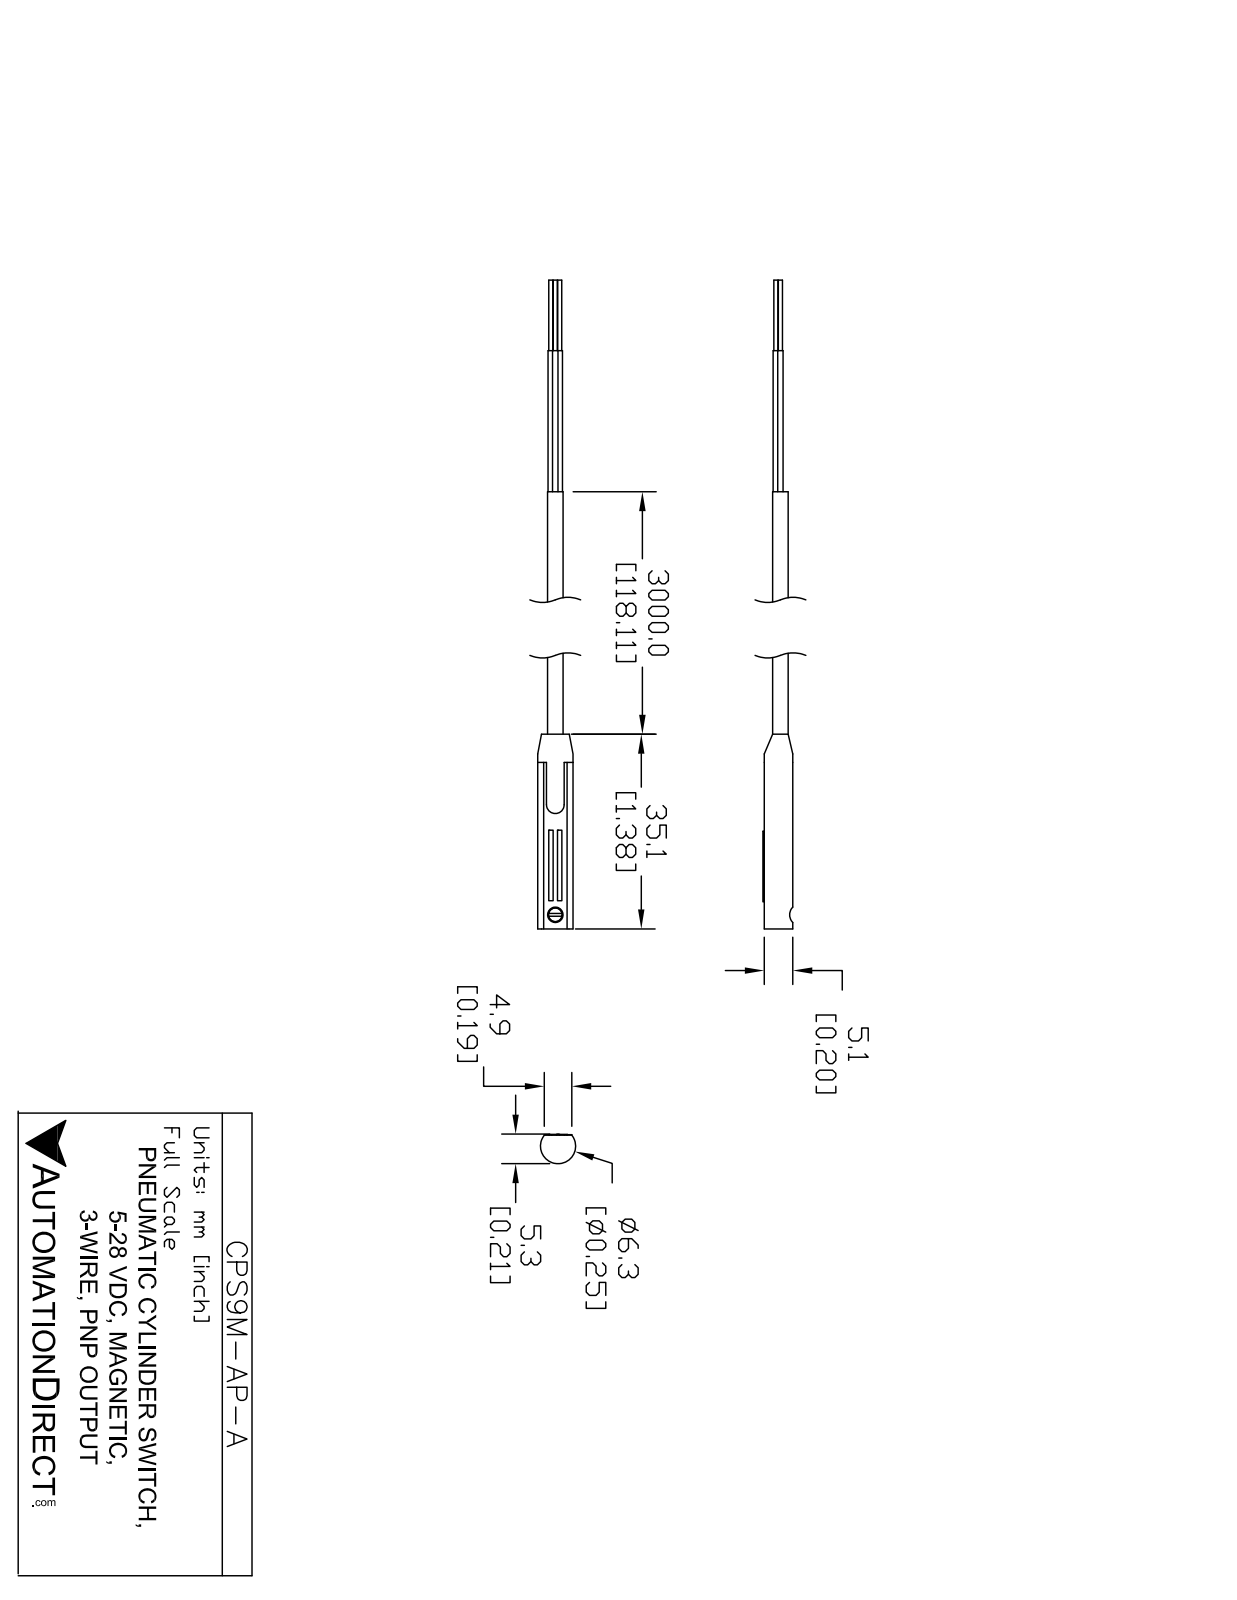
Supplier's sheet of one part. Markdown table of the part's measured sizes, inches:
| quantity | value |
| --- | --- |
| part name | CPS9M-AP-A |
| STEP written by | SolidWorks 2017 (AUTOMOTIVE_DESIGN) |
| units | inches |
| bodies | 4 solids, 122 faces (48 planar, 50 cylindrical, 24 other) |
| overall size | 5.682 × 0.25 × 0.21 |
| volume | 0.075 in³ |
| surface area | 3.88 in² |
| round holes (diameter × count) | 0.031 × 1, 0.104 × 1 |
| round bosses / shafts (diameter × count) | 0.138 × 1, 0.105 × 1 |
| partial cylindrical surfaces (radius × count) | 0.005 × 13, 0.015 × 3, 0.031 × 2, 0.045 × 1, 0.062 × 1, 0.105 × 1, 0.125 × 1 |
| main face-to-face distances | 0.168, 0.02, 0.021, 0.146, 0.062, 0.042, 0.029, 0.071, 0.091, 1.18 |
| hole center spacings | 0.136 |
